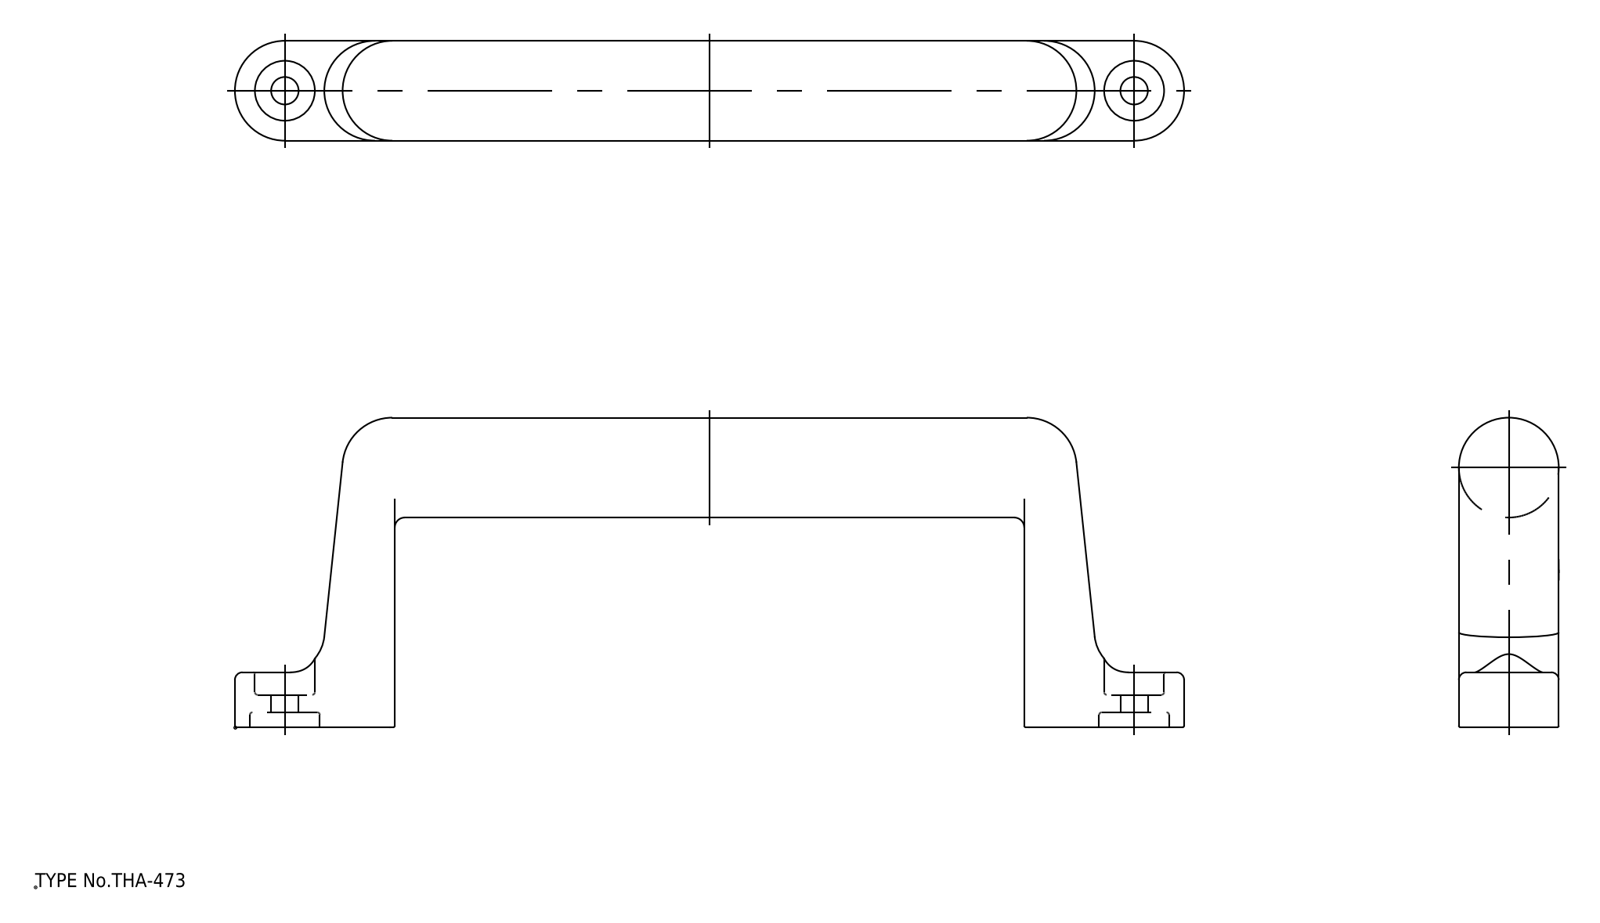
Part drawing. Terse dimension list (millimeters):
written by: spGate 17.5.1 (AUTOMOTIVE_DESIGN)
unit: mm
bodies: 1 solid, 80 faces (14 planar, 32 cylindrical, 34 other)
size: 190 × 62 × 20
volume: 70 624 mm³; area: 17 247 mm²
holes: 2× ⌀5.5, 2× ⌀12, 2× ⌀14
bosses: 1× ⌀20
rounds: 4× R0.3, 4× R1, 4× R10, 2× R1.5
face distances: 126, 20, 3, 6.5, 3.5, 11, 8, 4.5
hole spacings: 170
